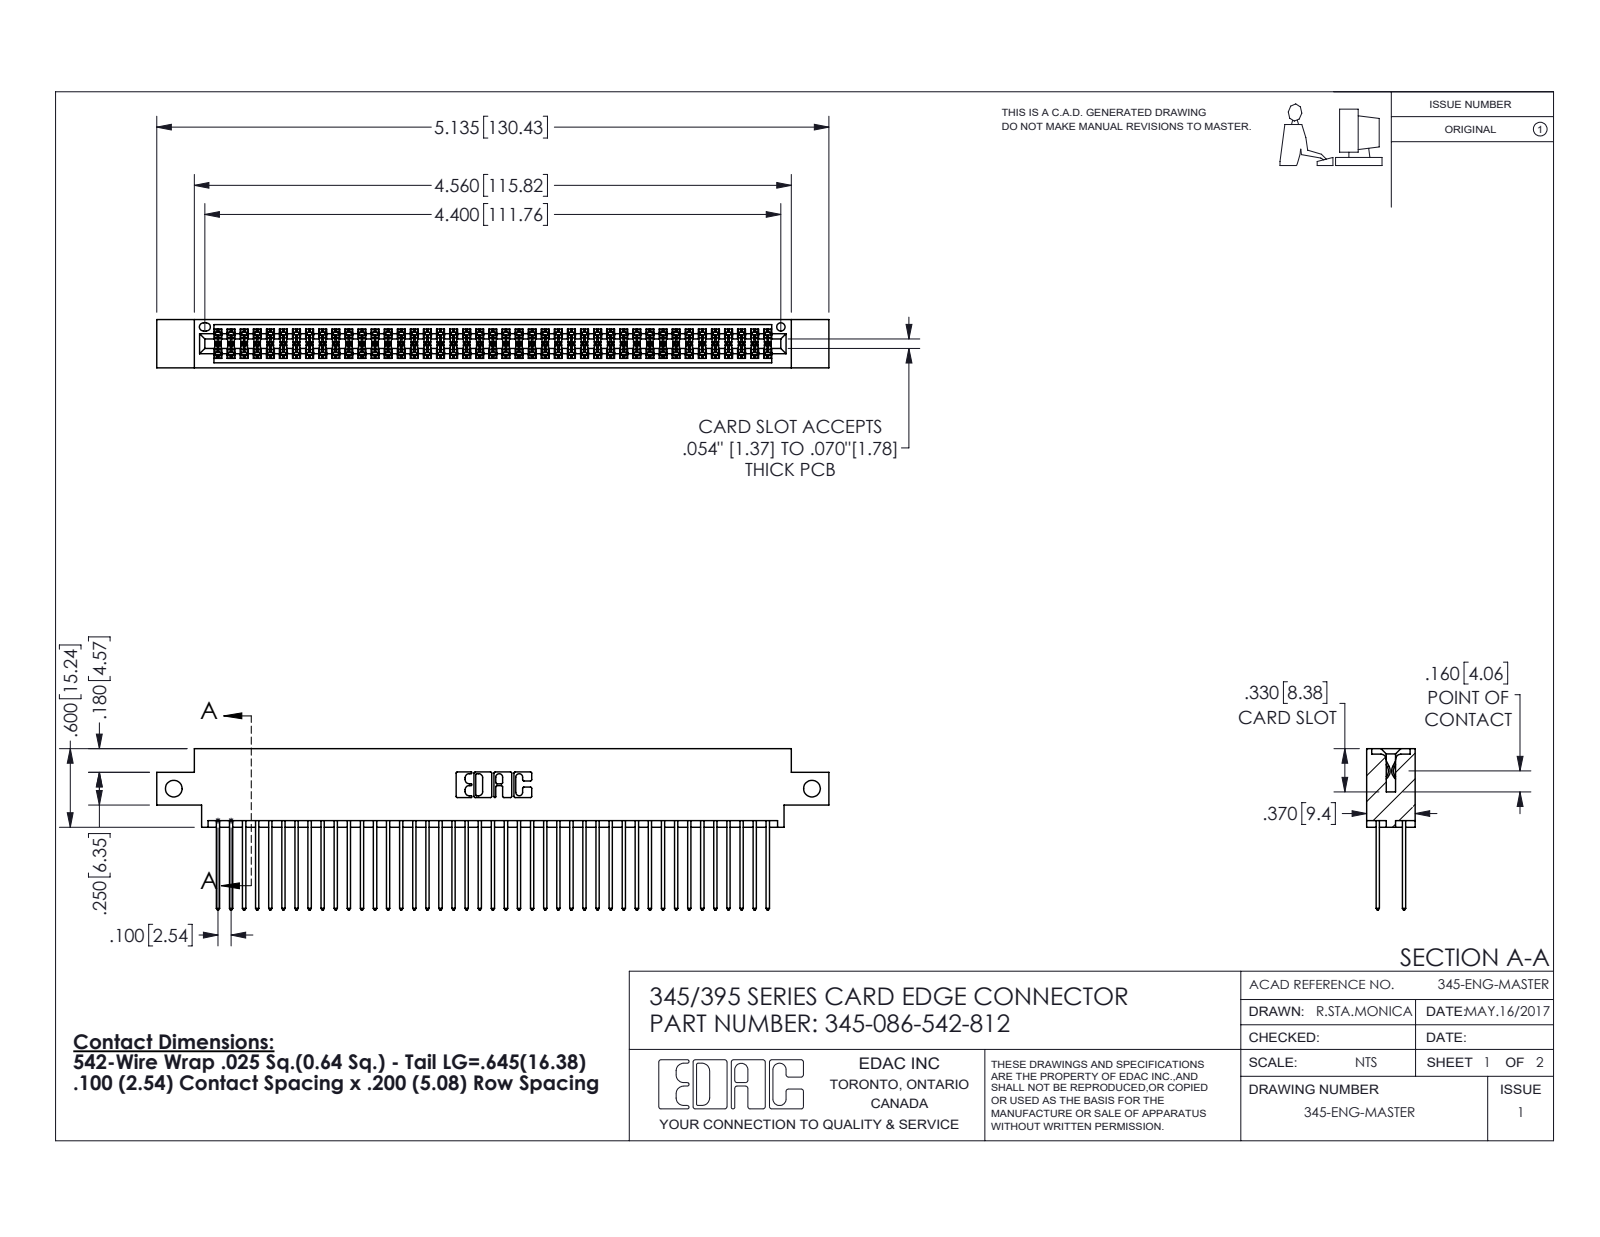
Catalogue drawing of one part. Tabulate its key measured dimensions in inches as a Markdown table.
| quantity | value |
| --- | --- |
| part name | 345-292-001_345-293-142; 345-086-542-812; 345 Part_0.170 Offset - Side Mount |
| STEP written by | SolidWorks 2016 (CONFIG_CONTROL_DESIGN) |
| units | inches |
| bodies | 87 solids, 4430 faces (2922 planar, 1508 cylindrical, 0 other) |
| overall size | 5.135 × 1.232 × 0.37 |
| volume | 0.786 in³ |
| surface area | 32.46 in² |
| round holes (diameter × count) | 0.128 × 2, 0.064 × 1 |
| partial cylindrical surfaces (radius × count) | 0.006 × 129, 0.01 × 86, 0.01 × 22, 0.007 × 6, 0.031 × 6, 0.026 × 3, 0.014 × 2, 0.019 × 2 |
| main face-to-face distances | 0.298, 0.072, 0.2, 0.098, 0.272, 0.025, 0.37, 0.225, 0.175, 0.149 |
| hole center spacings | 4.875 |
